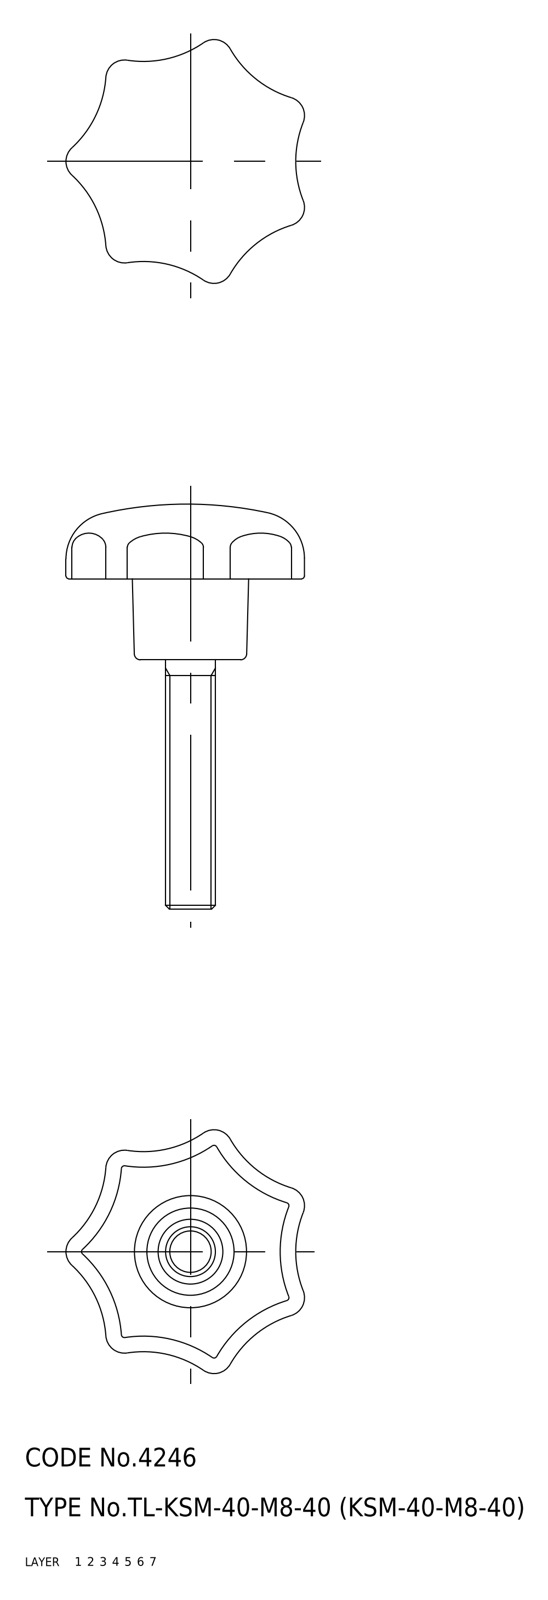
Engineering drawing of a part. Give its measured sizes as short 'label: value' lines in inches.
name: screw; knob; KSM_40_M8_40_9299_36
written by: CADfix (AUTOMOTIVE_DESIGN)
unit: in
bodies: 2 solids, 103 faces (0 planar, 0 cylindrical, 103 other)
size: 2.559 × 1.541 × 1.509
volume: 0.764 in³; area: 10.78 in²
